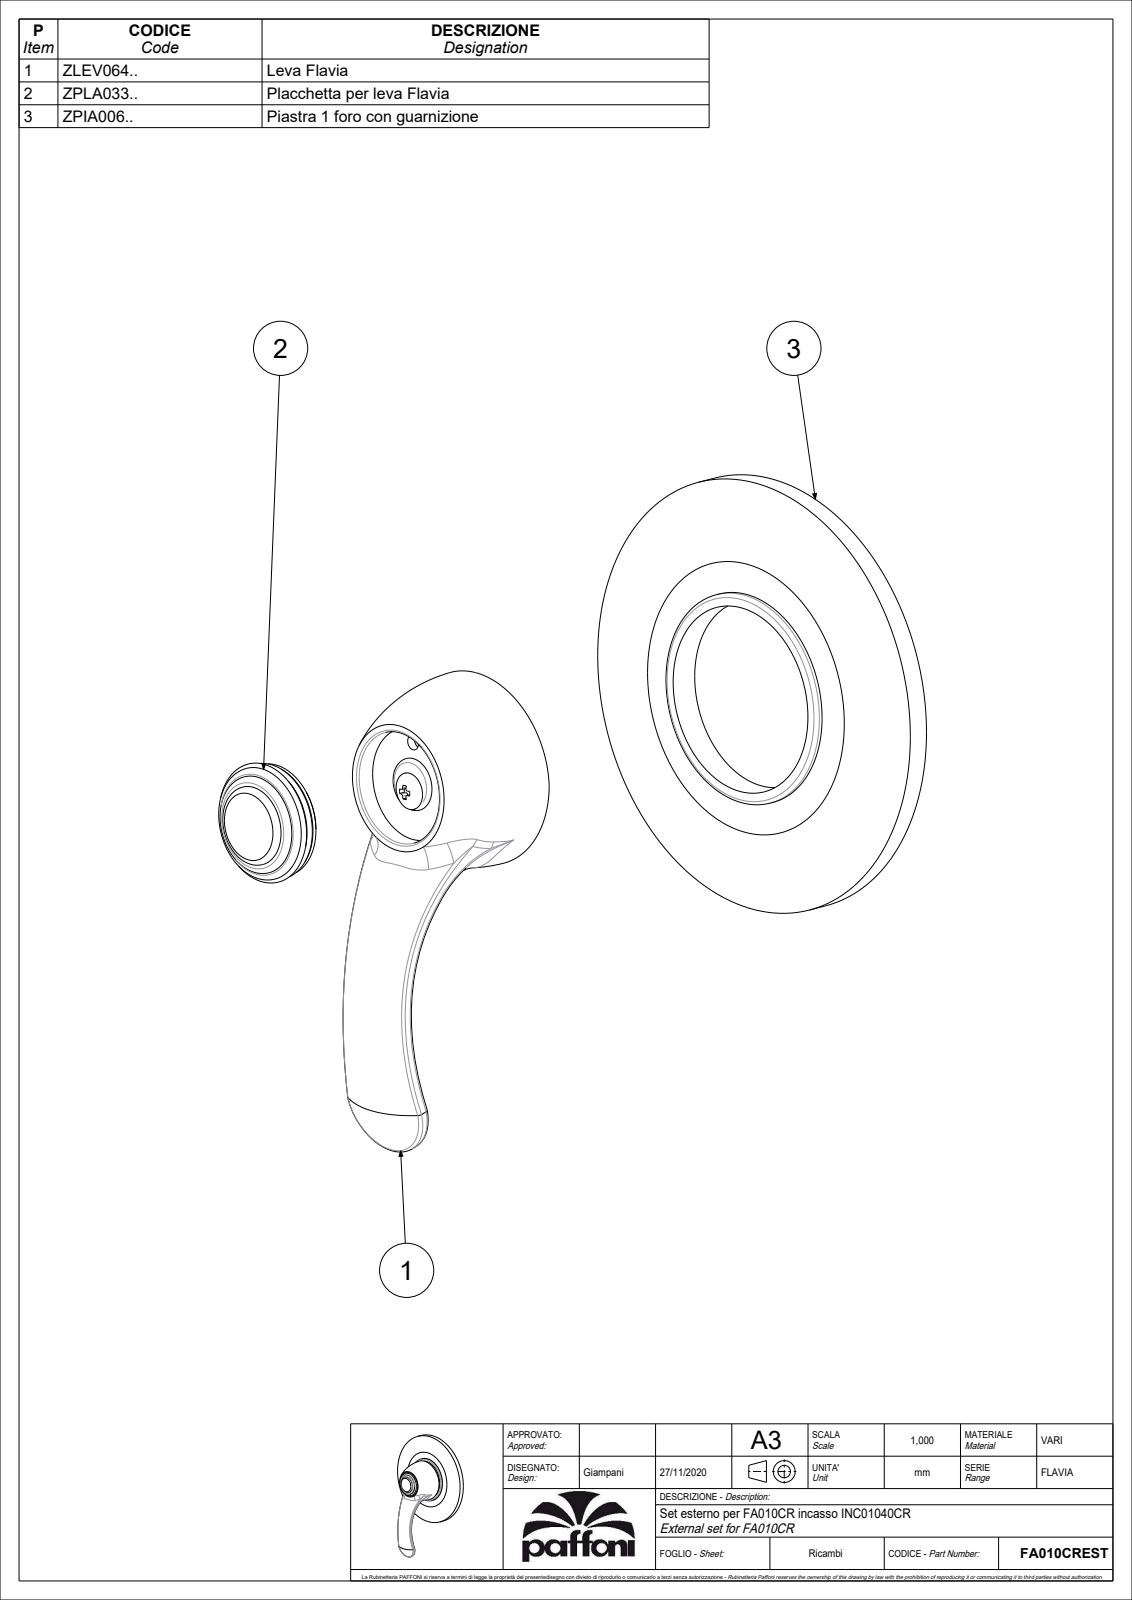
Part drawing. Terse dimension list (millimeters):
name: FA010CREST
written by: CREO PARAMETRIC BY PTC INC, 2020044 (CONFIG_CONTROL_DESIGN)
unit: mm
bodies: 2 solids, 236 faces (131 planar, 34 cylindrical, 71 other)
size: 156.3 × 116 × 55.53
volume: 43 210 mm³; area: 44 223 mm²
holes: 1× ⌀4, 1× ⌀7, 1× ⌀30, 1× ⌀50, 1× ⌀115
bosses: 1× ⌀116, 1× ⌀56.5, 1× ⌀55, 1× ⌀29.9, 1× ⌀27, 1× ⌀9.8, 1× ⌀4
rounds: 4× R0.5, 4× R1.5
face distances: 2.5, 35, 32, 8, 3, 9, 34.5, 6, 24, 26.5
hole spacings: 1.62, 11.38, 13
